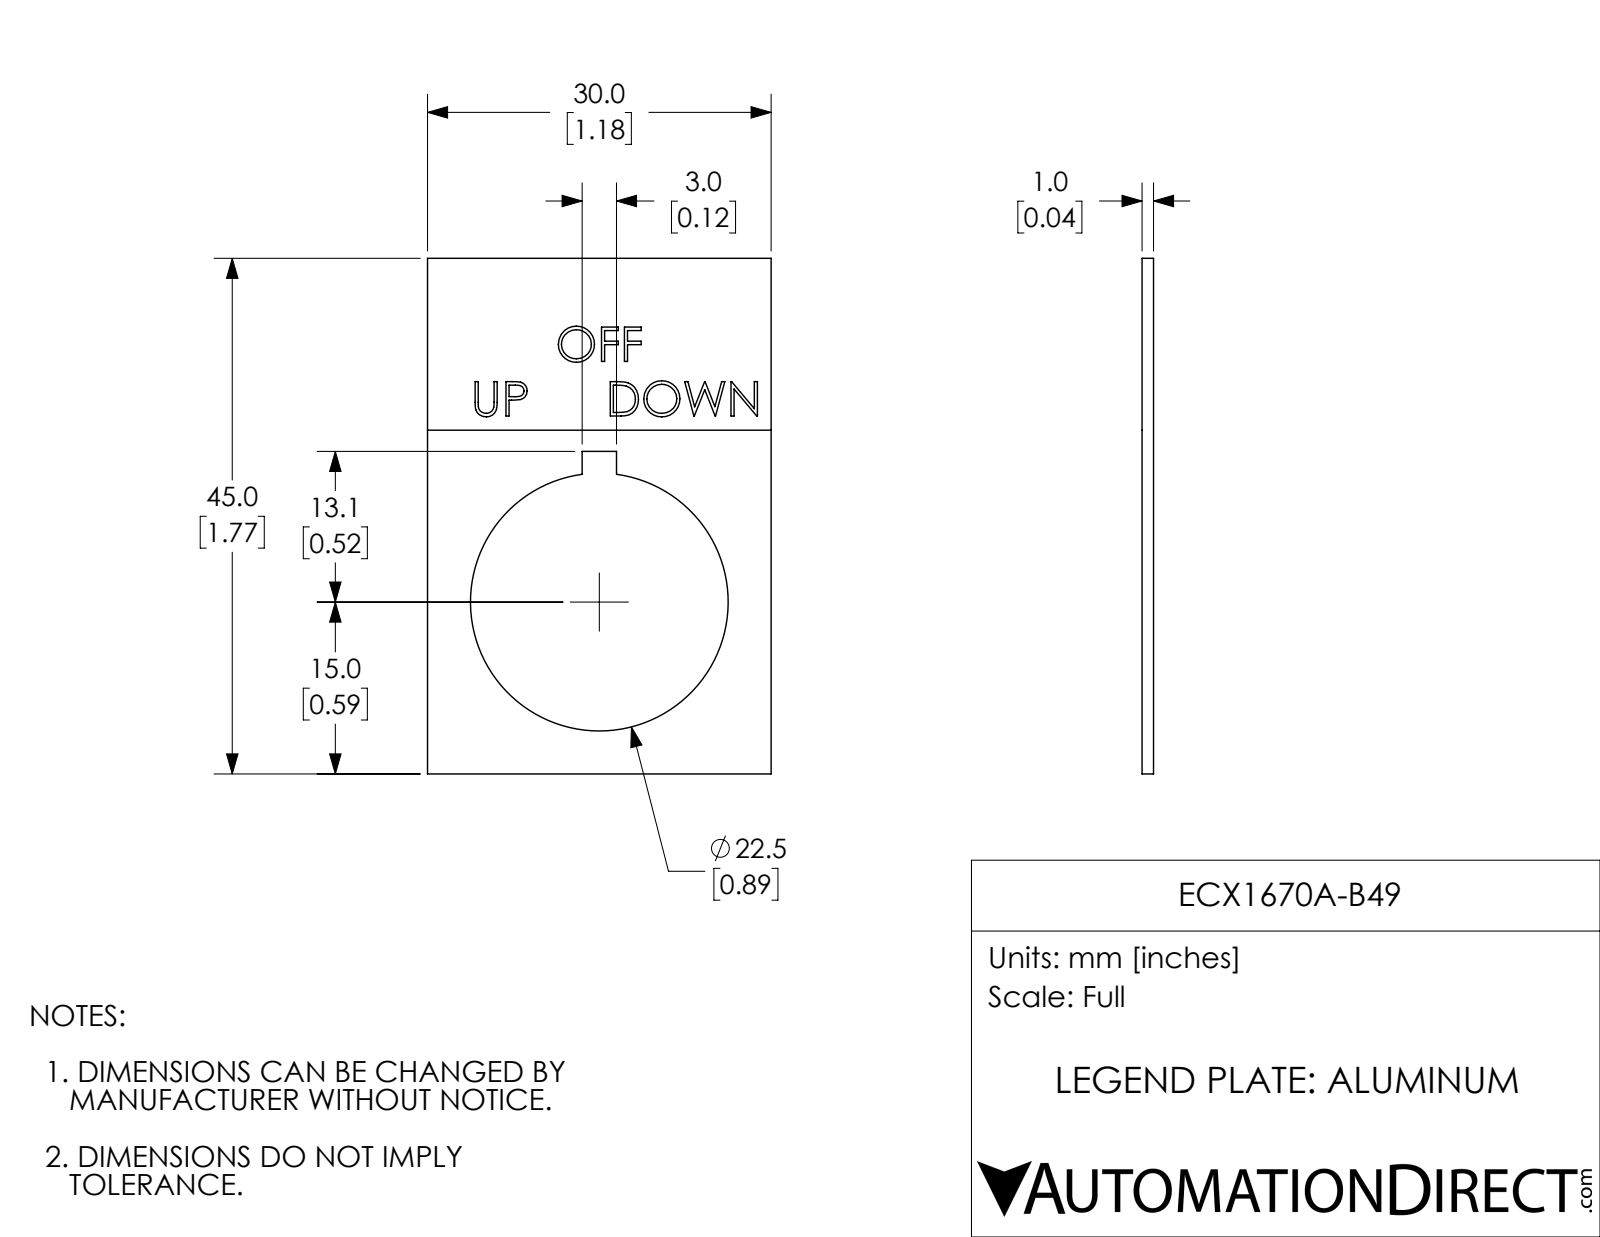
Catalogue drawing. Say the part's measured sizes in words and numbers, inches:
The part is named "ECX1670A-B49". Its 3-D file was written by "SolidWorks 2017 (AUTOMOTIVE_DESIGN)". It is 1 solid with 125 faces: 86 planar, 3 cylindrical and 36 other. Overall it measures 1.772 by 1.181 by 0.039 inches. Its volume is 0.058 cubic inches and its surface area 3.288 square inches. Round holes: 1 of diameter 0.886. The main face-to-face distances are 0.039, 1.181, 1.772, 0.038, 0.531, 0.65, 1.108, 0.663, 0.118, 0.048.
